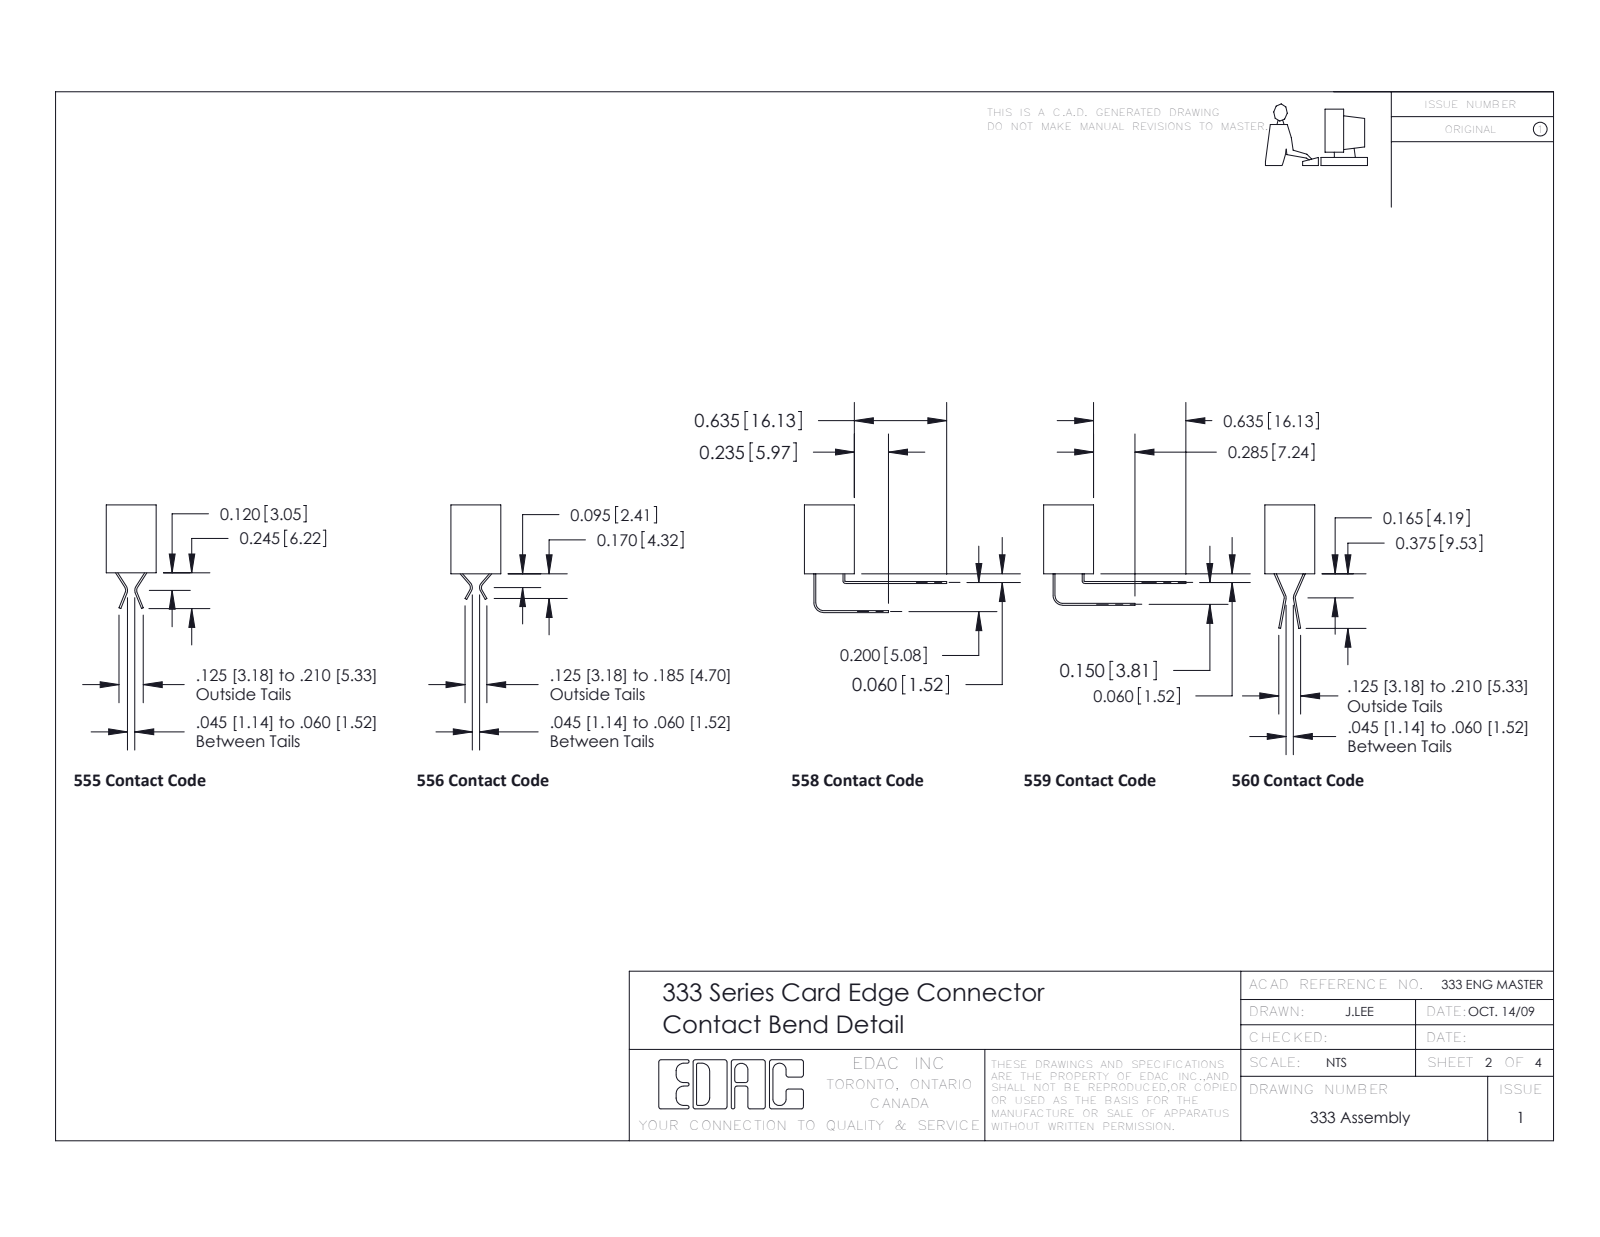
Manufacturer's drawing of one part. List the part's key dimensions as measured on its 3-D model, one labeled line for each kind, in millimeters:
Part name (STEP PRODUCT): 345-292-001_558 559 Tail - 1; 333-018-558-804; 345-292-001_558 Tail - 2; 333 Part_Offset - .156 Dia - TH
STEP written by: SolidWorks 2016 (CONFIG_CONTROL_DESIGN)
Units: millimetres
Bodies: 19 solids, 1090 faces (758 planar, 332 cylindrical, 0 other)
Overall size (bounding box): 57.2 × 25.5 × 22.2
Volume: 5 330 mm³ · Surface area: 6 471 mm²
Round holes (diameter × count): ⌀4 ×2
Partial cylindrical surfaces — rounded edges, fillets, slot ends (radius × count): R0.2 ×27, R0.3 ×22, R0.2 ×6, R0.8 ×6, R0.7 ×3, R0.4 ×2, R0.6 ×2, R0.6 ×2
Main face-to-face distances: 9.4, 4, 7.6, 1.3, 1.9, 1.8, 7.9, 3.8, 5.6, 3.8
Hole centre spacings: 50.9
